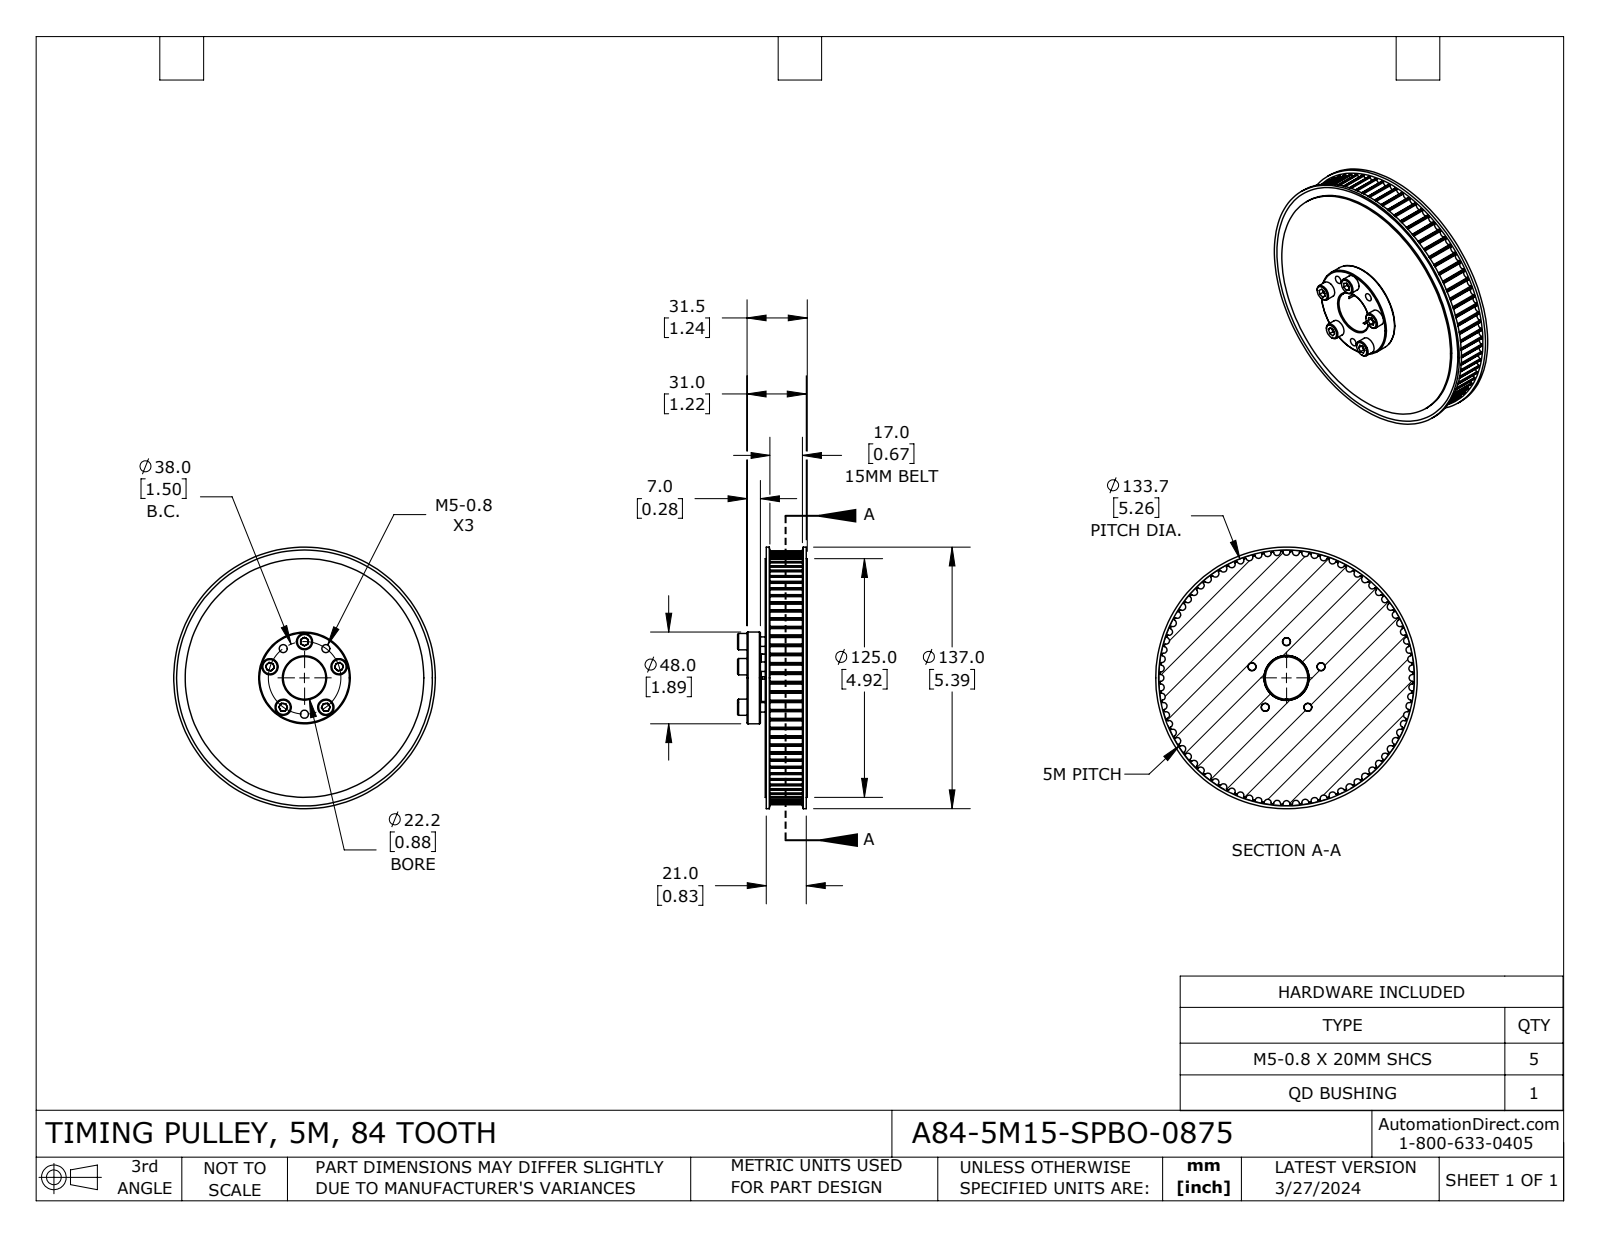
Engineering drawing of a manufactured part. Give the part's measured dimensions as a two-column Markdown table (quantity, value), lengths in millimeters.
| quantity | value |
| --- | --- |
| part name | A84-5M15-SPBO-0875 |
| STEP written by | SolidWorks 2021 (CONFIG_CONTROL_DESIGN) |
| units | millimeters |
| bodies | 9 solids, 654 faces (101 planar, 487 cylindrical, 66 other) |
| overall size | 137 × 137 × 36.5 |
| volume | 297 717 mm³ |
| surface area | 63 224 mm² |
| round holes (diameter × count) | 4.2 × 8, 5.5 × 5, 22.22 × 1, 24.83 × 1, 125 × 1 |
| round bosses / shafts (diameter × count) | 8.5 × 5, 5 × 5, 137 × 1, 48 × 1, 24.82 × 1 |
| partial cylindrical surfaces (radius × count) | 0.3 × 168, 1.82 × 84, 66.28 × 1 |
| main face-to-face distances | 22, 2.5, 19.5, 0.9, 21.1, 1.6, 18.6, 17, 20.2, 12 |
| hole center spacings | 19, 36.14, 30.74, 11.75, 22.34, 38, 11.74, 22.33 |
